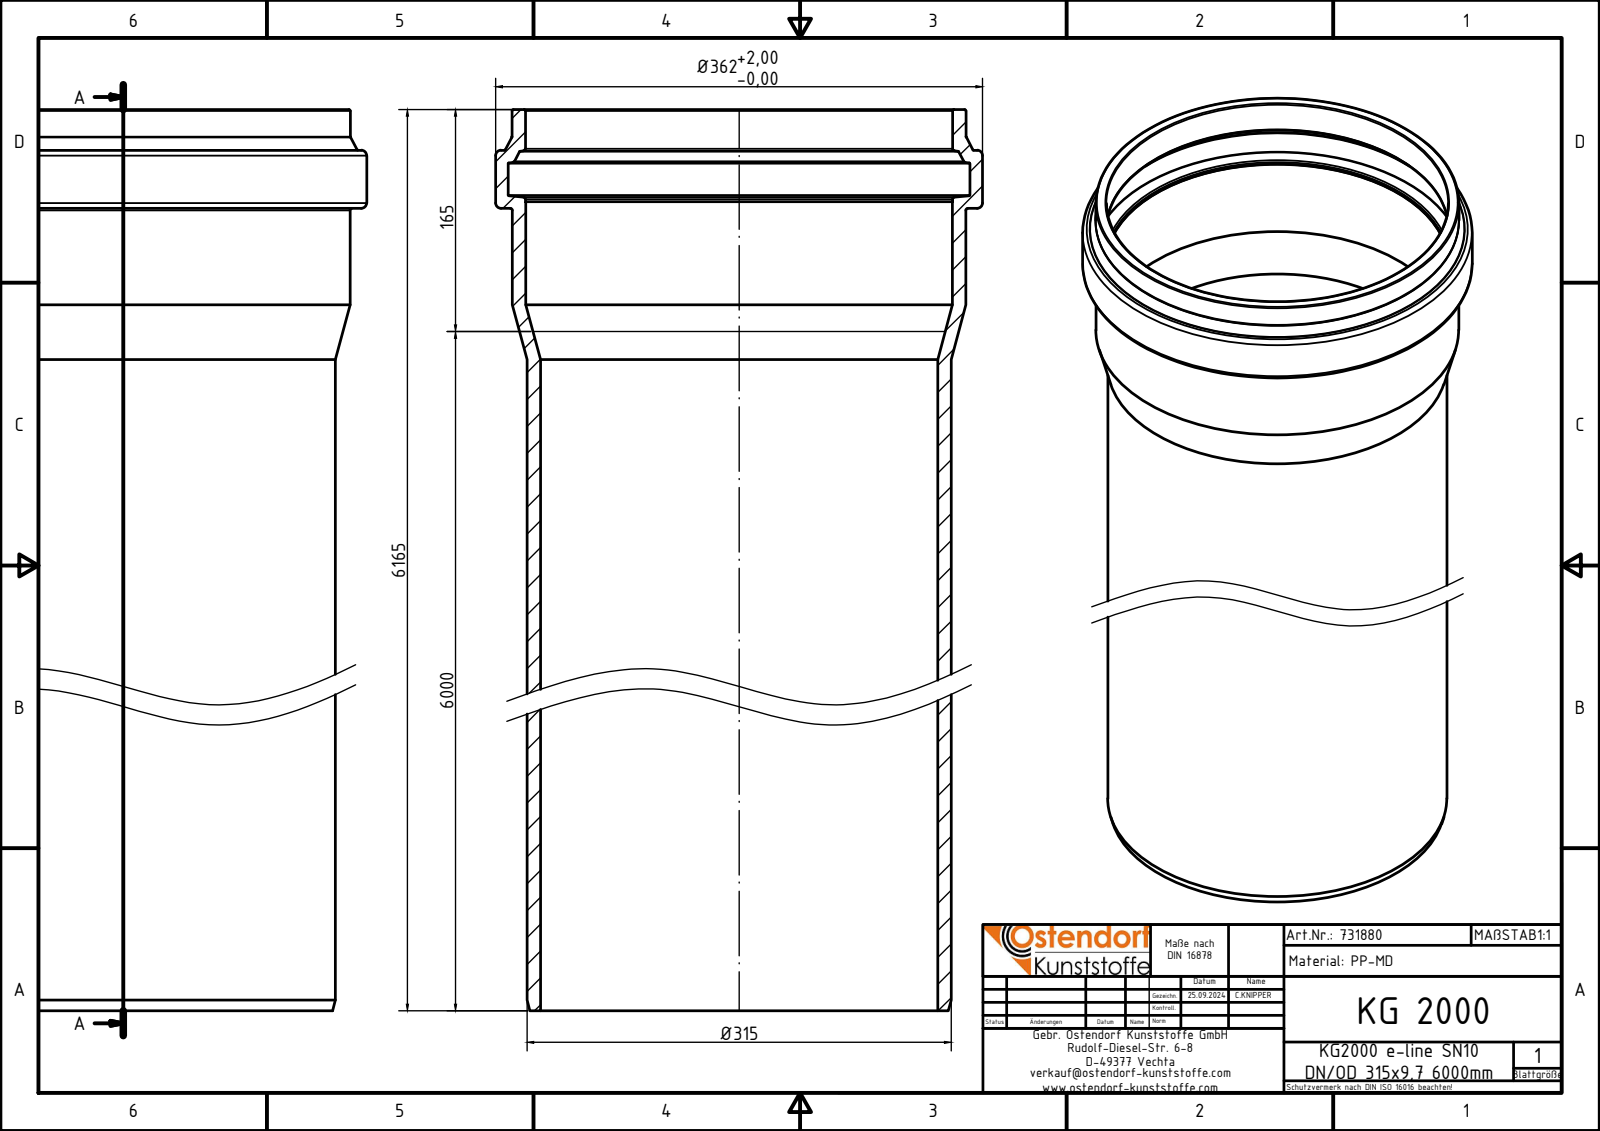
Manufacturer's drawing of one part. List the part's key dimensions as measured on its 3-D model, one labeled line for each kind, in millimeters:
Part name (STEP PRODUCT): 731880z
STEP written by: Autodesk Inventor 2024 (AUTOMOTIVE_DESIGN)
Units: millimetres
Bodies: 1 solid, 36 faces (5 planar, 9 cylindrical, 22 other)
Overall size (bounding box): 6165 × 362 × 362
Volume: 59 440 000 mm³ · Surface area: 11 910 000 mm²
Round holes (diameter × count): ⌀295.3 ×1, ⌀317.1 ×1, ⌀317.5 ×1, ⌀343.2 ×1
Round bosses / shafts (diameter × count): ⌀362 ×1, ⌀337.5 ×1, ⌀337.1 ×1, ⌀315.3 ×1
Main face-to-face distances: 73.5, 6091.5, 6165, 6134.7, 43.2, 30.3, 6096.45, 4.95, 38.25, 68.55
